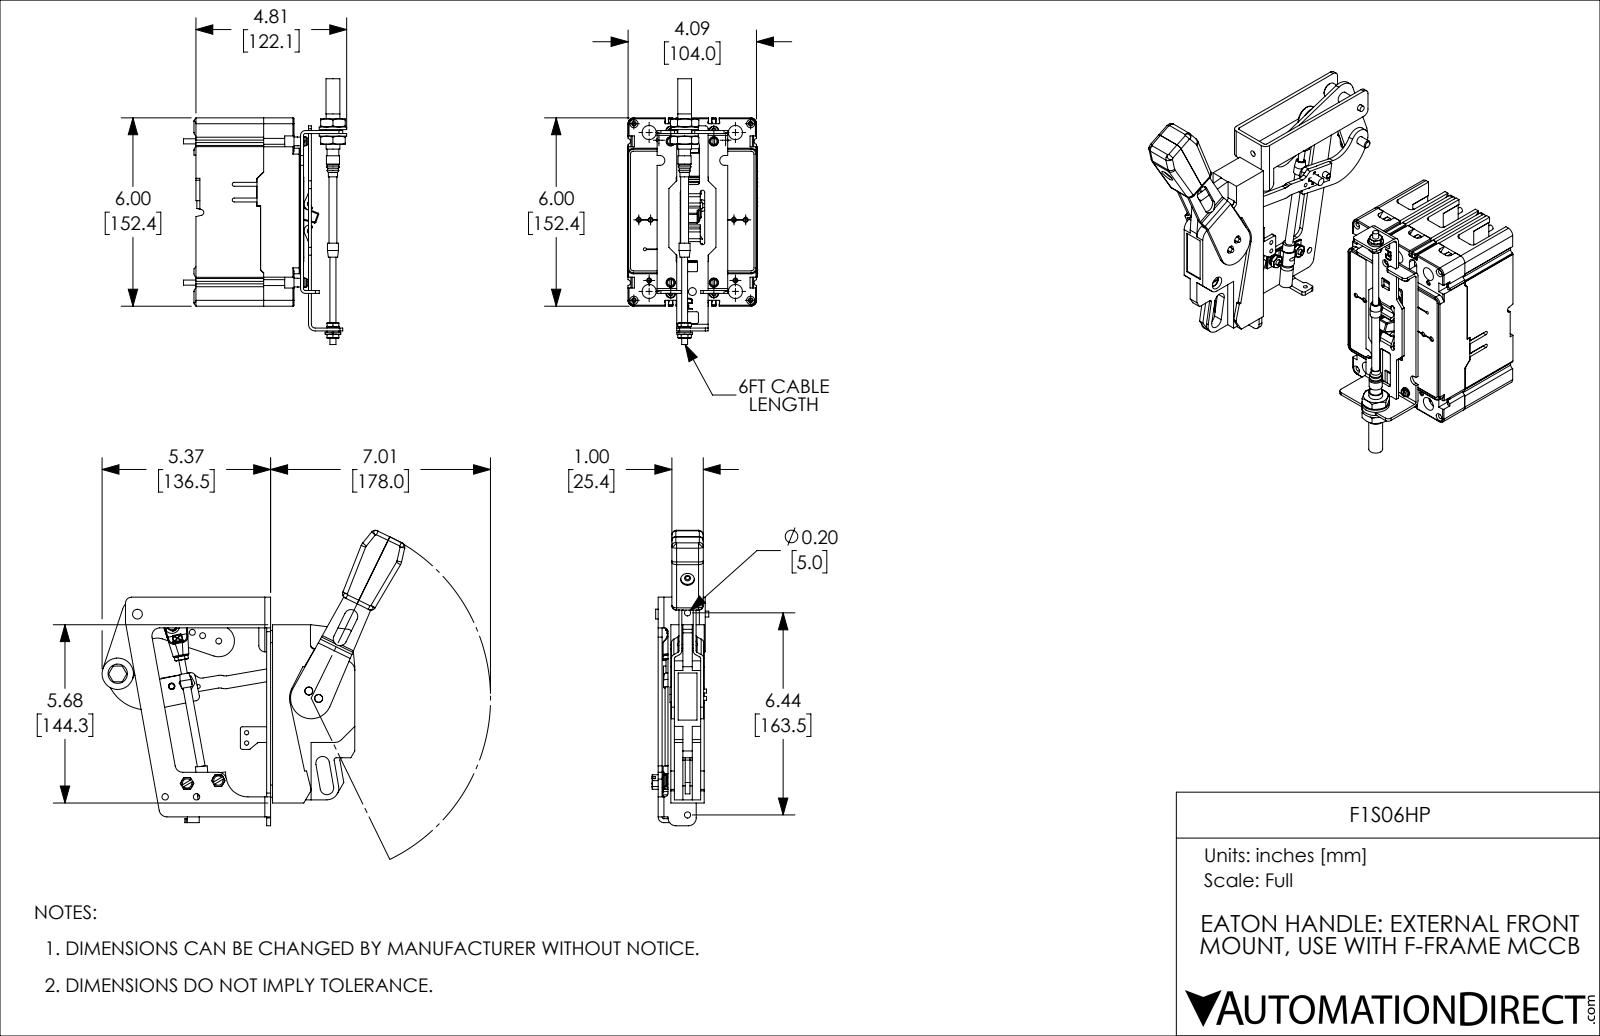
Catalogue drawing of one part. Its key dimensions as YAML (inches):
part_name: "F1S06HP_HANDLE; F1S06HP; F1S06HP_BREAKER"
step_written_by: "SolidWorks 2019 (CONFIG_CONTROL_DESIGN)"
units: inches
bodies: {solids: 82, faces: 4453, planar: 2368, cylindrical: 1637, other: 448}
overall_size: [10.091, 9.783, 9.651]
volume: 47.35
surface_area: 700.7
round_holes:
  - {diameter: 0.156, count: 12}
  - {diameter: 0.188, count: 11}
  - {diameter: 0.114, count: 8}
  - {diameter: 0.16, count: 8}
  - {diameter: 0.125, count: 6}
  - {diameter: 0.136, count: 6}
  - {diameter: 0.141, count: 6}
  - {diameter: 0.145, count: 6}
  - {diameter: 0.168, count: 6}
  - {diameter: 0.203, count: 6}
  - {diameter: 0.45, count: 6}
  - {diameter: 0.11, count: 5}
round_bosses_or_shafts:
  - {diameter: 0.25, count: 8}
  - {diameter: 0.297, count: 6}
  - {diameter: 0.164, count: 6}
  - {diameter: 0.418, count: 4}
  - {diameter: 0.375, count: 4}
  - {diameter: 0.281, count: 4}
  - {diameter: 0.27, count: 4}
  - {diameter: 0.219, count: 4}
partial_cylinders:
  - {radius: 0.031, count: 115}
  - {radius: 0.06, count: 67}
  - {radius: 0.062, count: 56}
  - {radius: 0.125, count: 56}
  - {radius: 0.03, count: 50}
  - {radius: 0.032, count: 38}
  - {radius: 0.09, count: 33}
  - {radius: 0.12, count: 23}
face_to_face_distances: [0.125, 0.125, 0.187, 0.094, 0.247, 0.11, 0.95, 0.117, 2.126, 0.218]
hole_center_spacings: [4.83, 0.742, 1.375, 4.5, 0.344, 0.691, 0.743, 2.082]
